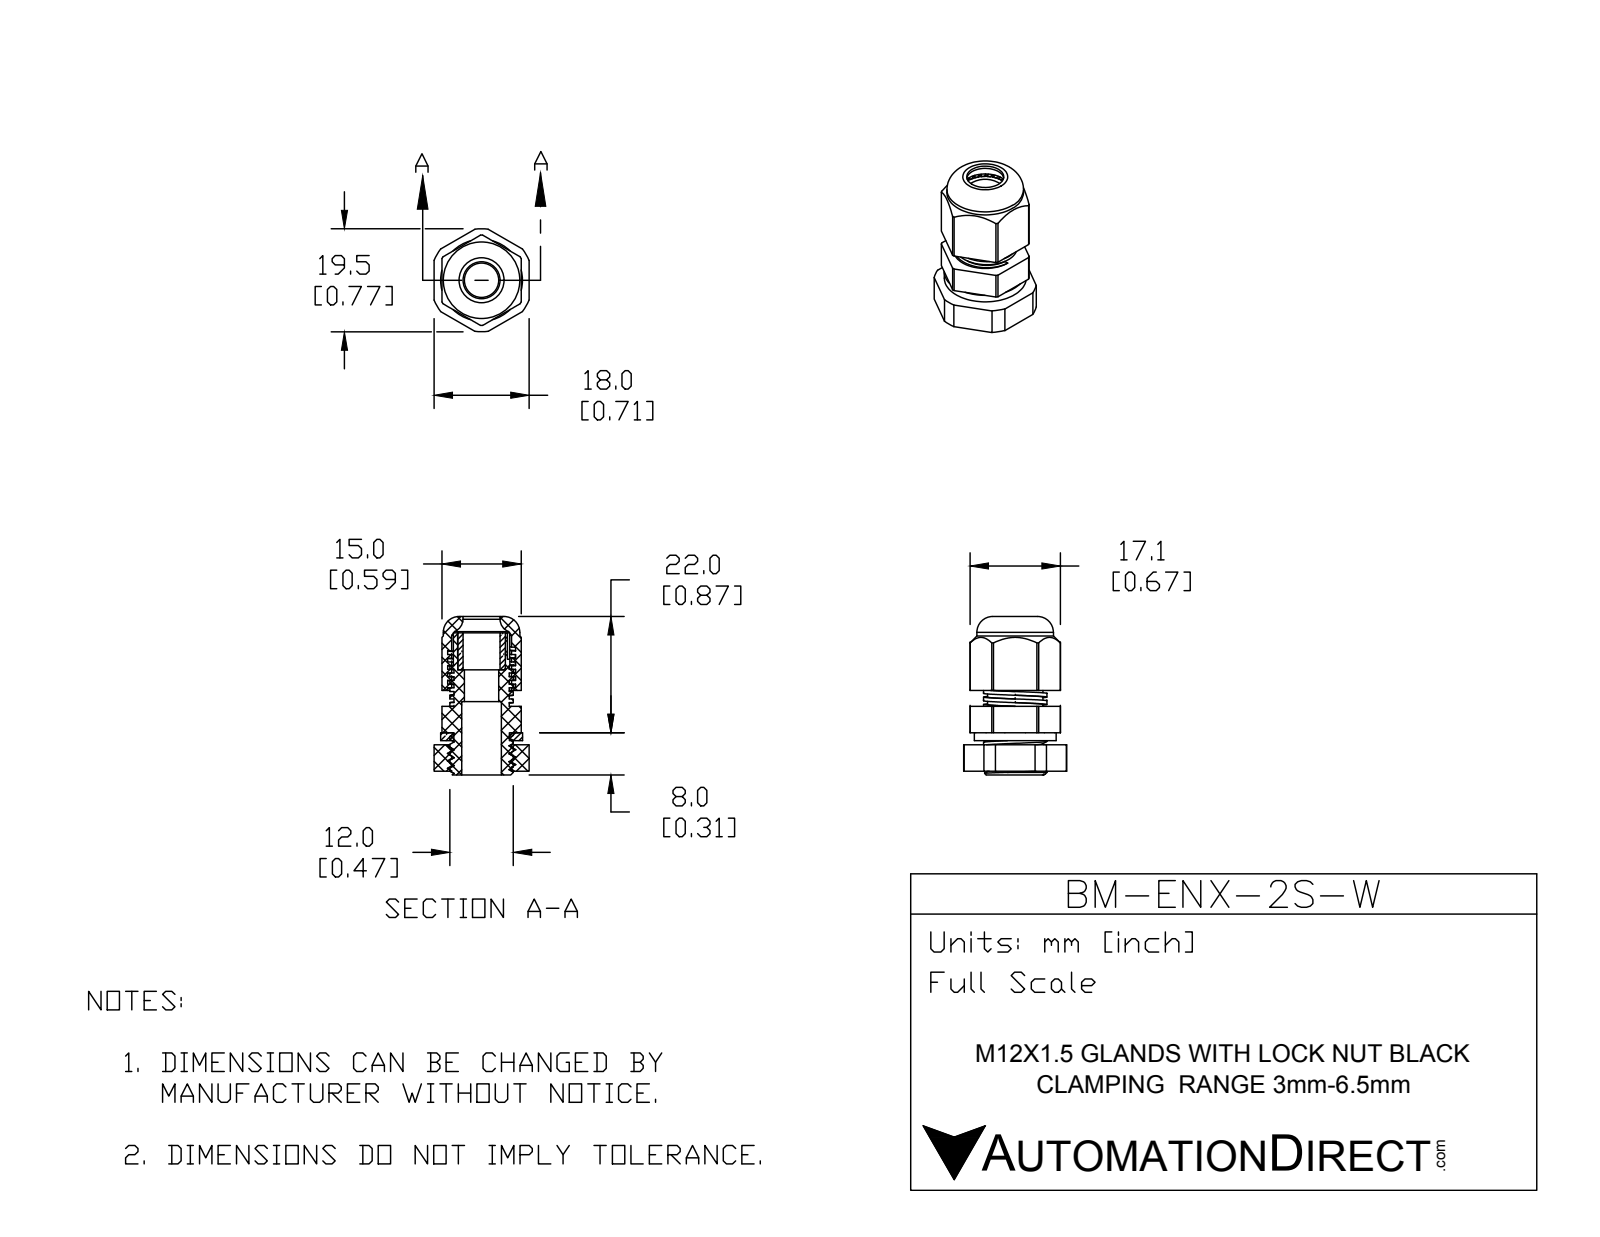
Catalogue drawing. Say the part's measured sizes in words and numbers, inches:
The part is named "BM-ENX-2S-W". Its 3-D file was written by "SolidWorks 2015 (CONFIG_CONTROL_DESIGN)". It is 5 solids with 244 faces: 134 planar, 88 cylindrical and 22 other. Overall it measures 1.181 by 0.768 by 0.709 inches. Its volume is 0.251 cubic inches and its surface area 9.249 square inches. Round holes: 1 of diameter 0.256, 1 of diameter 0.276, 1 of diameter 0.295, 1 of diameter 0.354, 1 of diameter 0.413, 1 of diameter 0.446. Round bosses or shafts: 1 of diameter 0.61, 1 of diameter 0.571, 1 of diameter 0.472, 1 of diameter 0.421. Partial cylindrical surfaces (rounded edges, fillets, slot ends): 1 of radius 0.337, 1 of radius 0.384. The main face-to-face distances are 0.591, 0.059, 0.197, 0.295, 0.65, 0.098, 0.02, 0.256, 0.315, 0.236.
